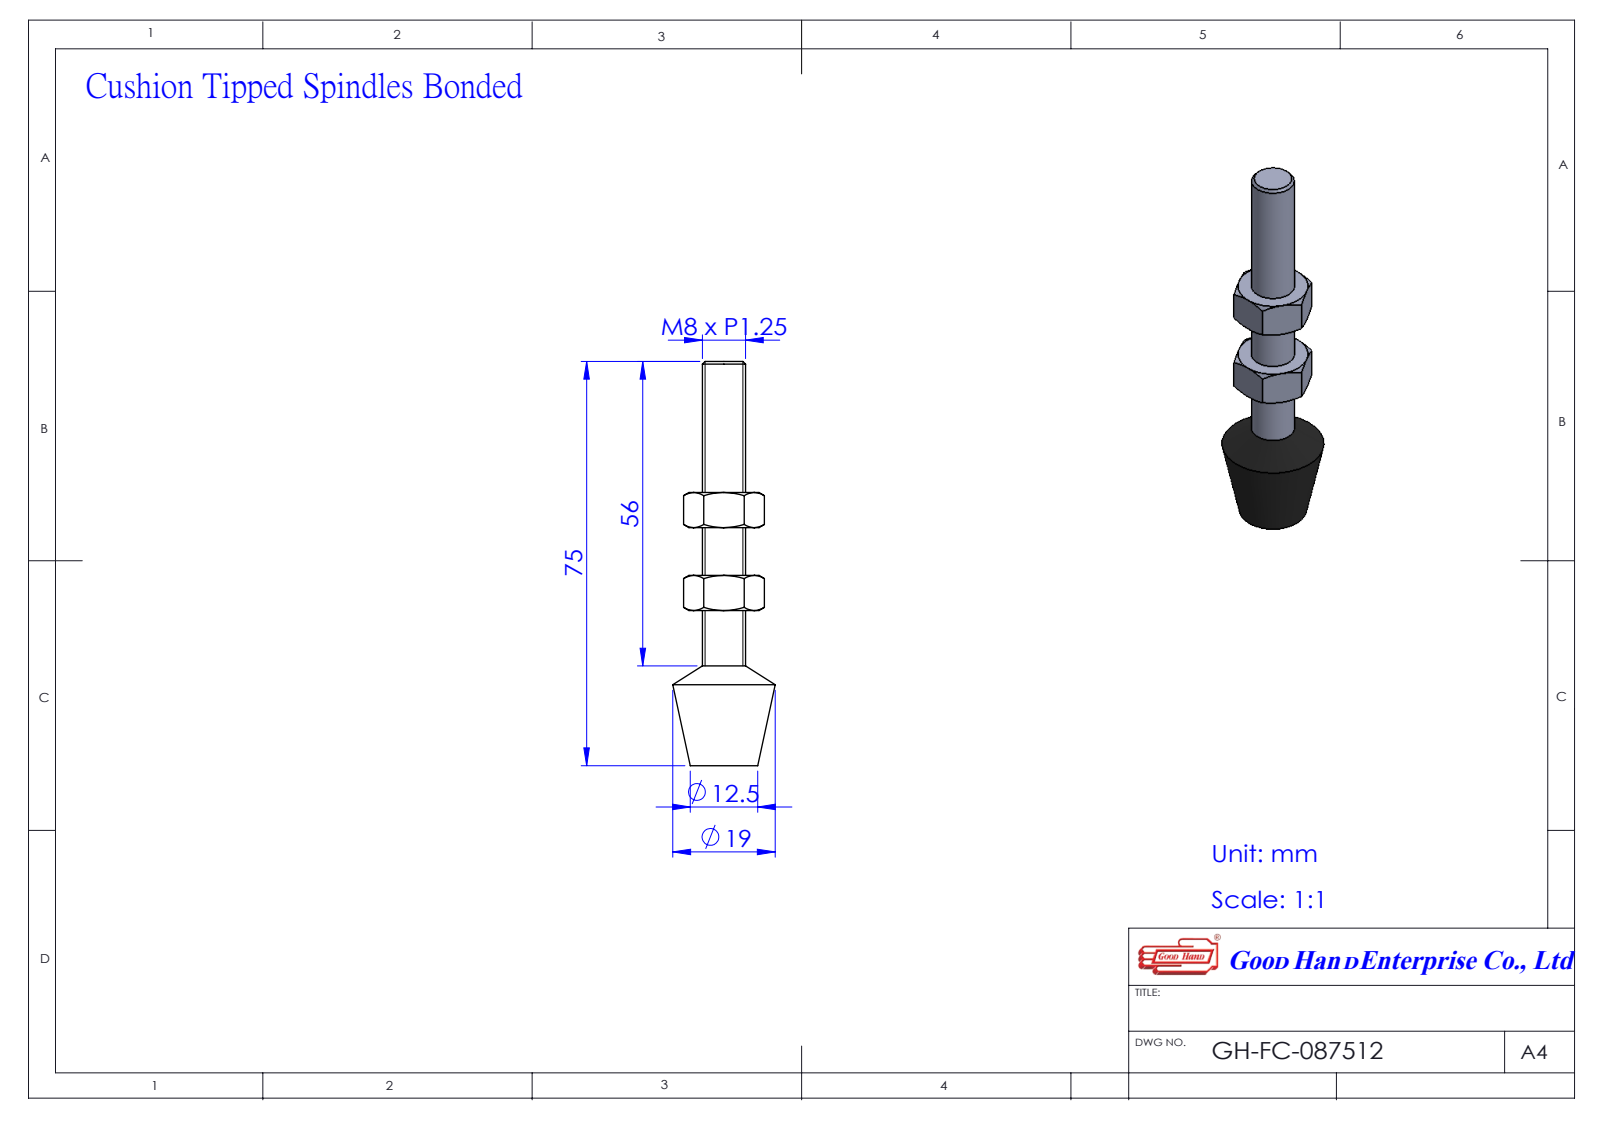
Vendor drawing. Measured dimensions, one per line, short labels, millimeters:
name: GH-FC-087512; 7408075; hexagon nut_2_jis_JIS B 1181 Hexagon nut - Class 2 Finished M8 --N
written by: SolidWorks 2016 (AUTOMOTIVE_DESIGN)
unit: mm
bodies: 3 solids, 66 faces (18 planar, 10 cylindrical, 38 other)
size: 75 × 19 × 19
volume: 7 738 mm³; area: 3 874 mm²
holes: 1× ⌀6.8, 1× ⌀8
face distances: 13, 15.39, 6.5, 35.28, 50.67, 28.78, 44.17, 21.89, 8.89, 75
